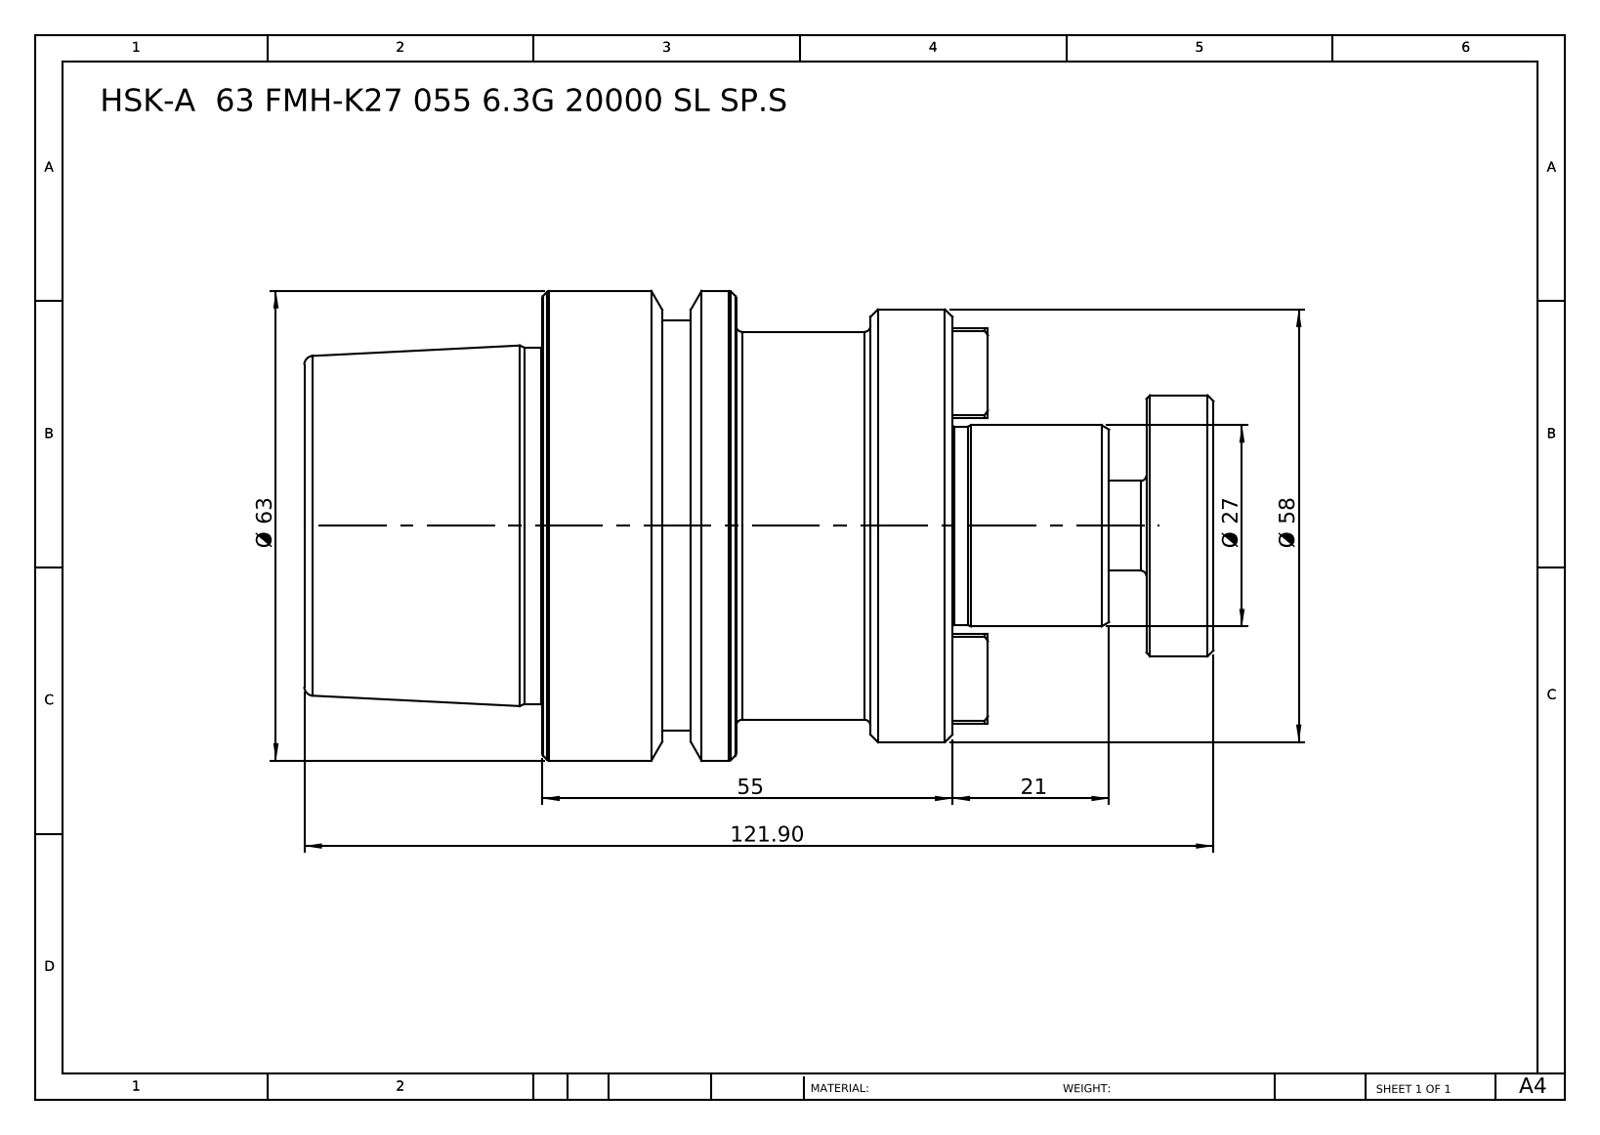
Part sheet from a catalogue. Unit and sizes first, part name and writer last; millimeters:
Units: millimetres
Overall size (bounding box): 121.9 × 63 × 63
Round bosses / shafts (diameter × count): ⌀63 ×1, ⌀58 ×1, ⌀55 ×1, ⌀52 ×1, ⌀47.78 ×1, ⌀35 ×1, ⌀27 ×1, ⌀26.6 ×1
Main face-to-face distances: 86.9, 26, 55, 35, 121.9, 9, 112.9, 29, 90, 81
Volume: 222 217 mm³ · Surface area: 27 295 mm²
Bodies: 1 solid, 106 faces (38 planar, 20 cylindrical, 48 other)
Part name (STEP PRODUCT): HSK-A 63 FMH27 055 6.3G 20000 SL SP
STEP written by: SolidWorks 2014 (CONFIG_CONTROL_DESIGN)
